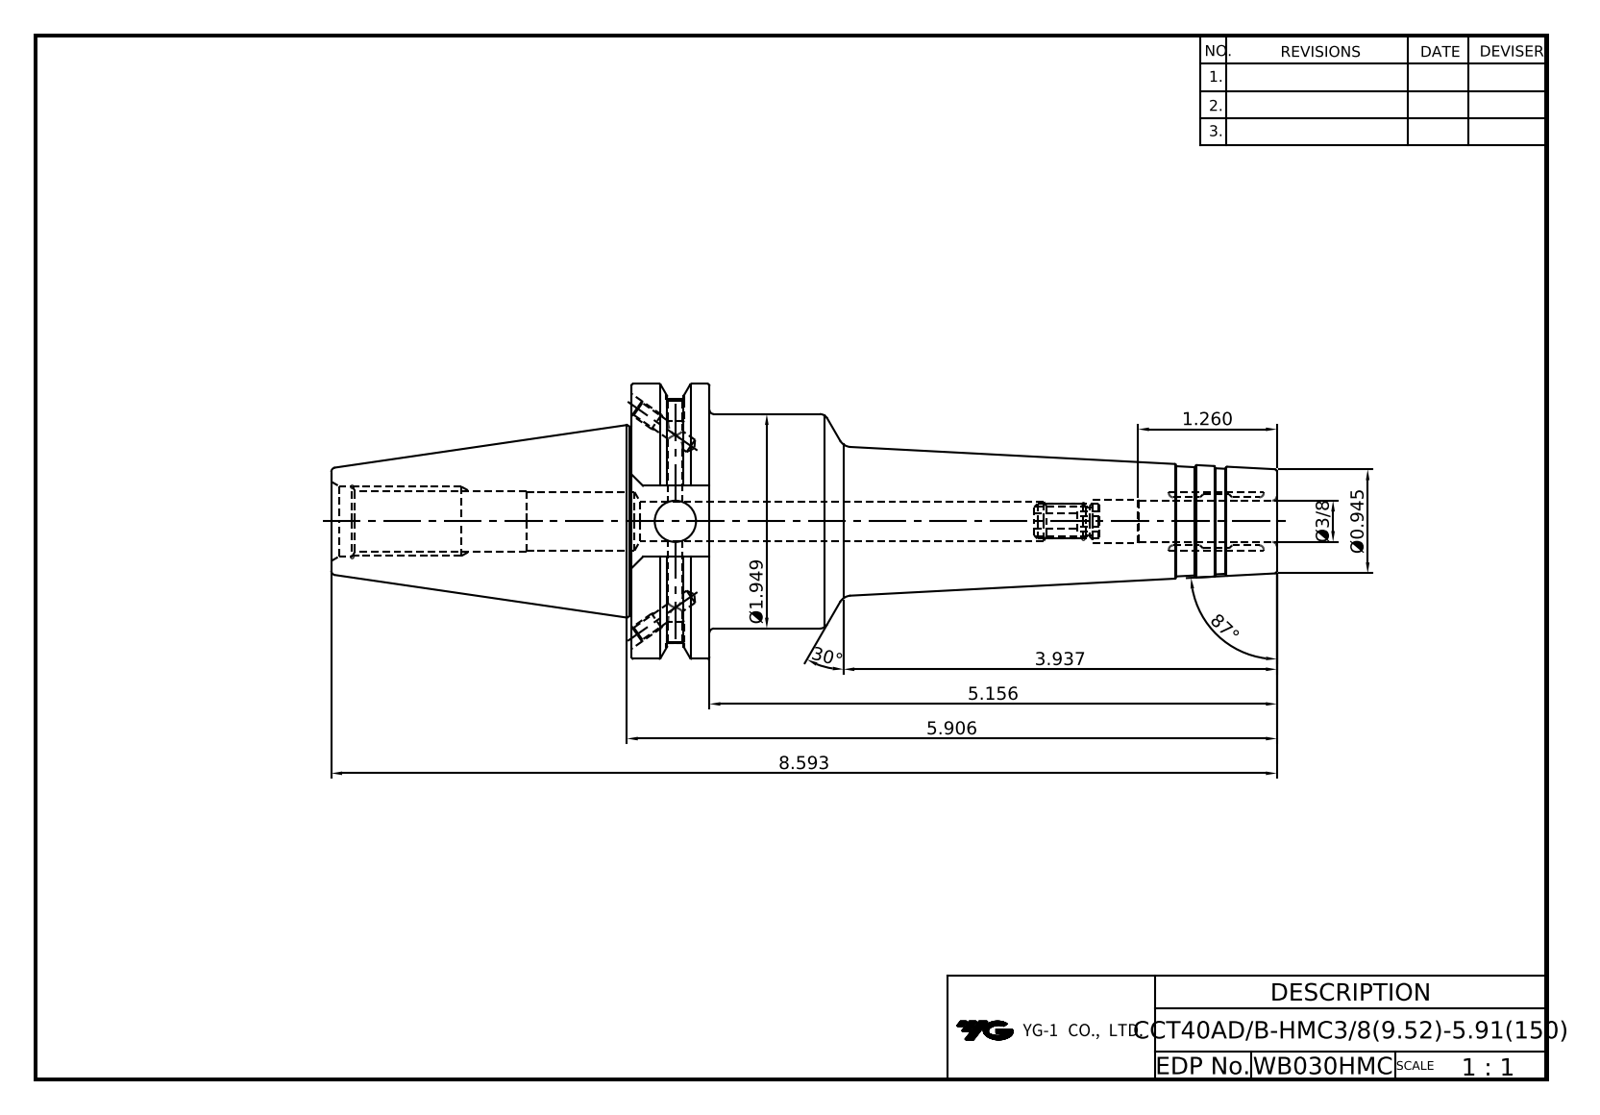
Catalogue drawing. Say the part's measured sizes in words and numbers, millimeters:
The part is named "LO-CCT40ADB-HMC9.525-150". Its 3-D file was written by "Autodesk Inventor 2025 (AUTOMOTIVE_DESIGN)". It is 1 solid with 105 faces: 36 planar, 29 cylindrical and 40 other. Overall it measures 218.25 by 63.5 by 61.09 millimeters. Its volume is 221 104 cubic millimeters and its surface area 37 553 square millimeters. Round holes: 4 of diameter 3.24, 2 of diameter 4, 2 of diameter 4.2, 2 of diameter 9.53, 1 of diameter 6.92, 1 of diameter 9, 1 of diameter 10, 1 of diameter 13.39, 1 of diameter 16.3. Round bosses or shafts: 1 of diameter 63.5, 1 of diameter 49.5. Partial cylindrical surfaces (rounded edges, fillets, slot ends): 1 of radius 8.19, 1 of radius 28.15. The main face-to-face distances are 18.05, 149, 130.95, 47.6, 16.38, 69.25, 87.3, 218.25, 81.3, 12.05.
